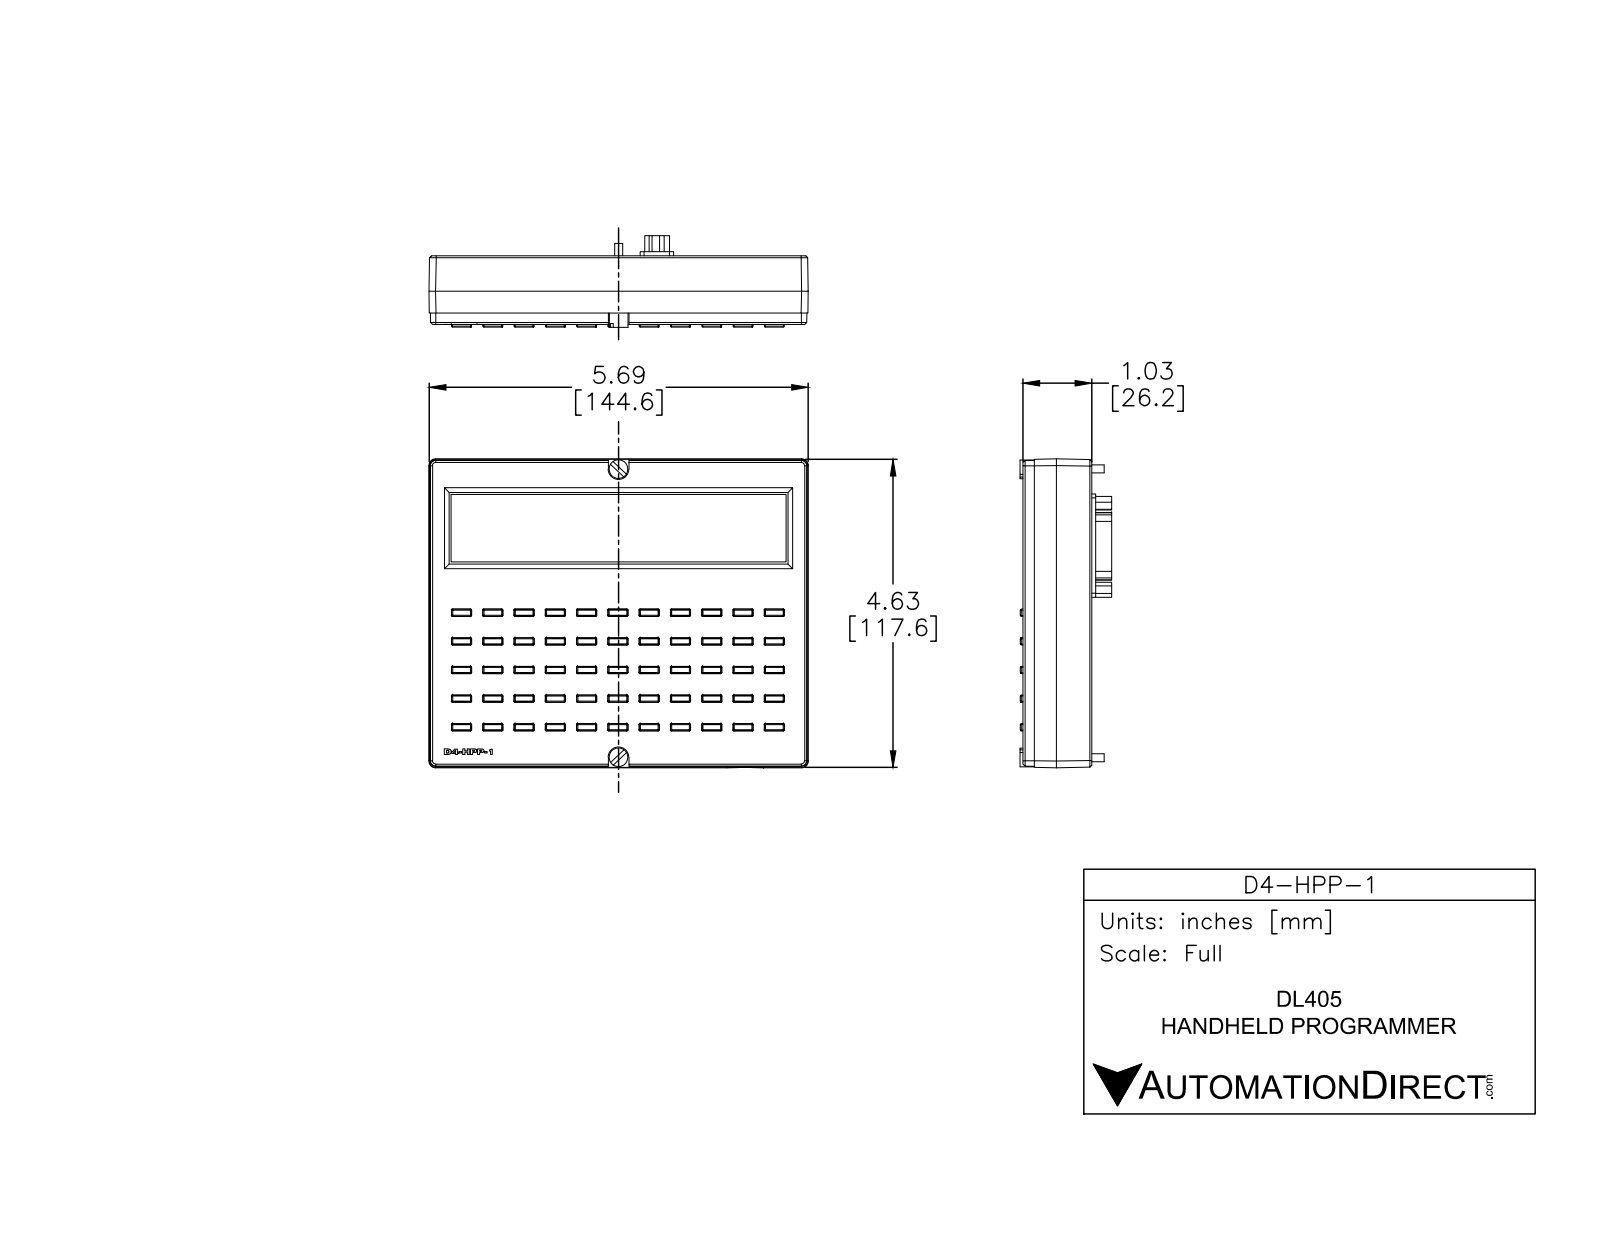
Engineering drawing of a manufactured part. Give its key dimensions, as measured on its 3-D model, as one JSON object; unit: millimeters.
{"part_name": "D4-HPP-1", "step_written_by": "SolidWorks 2014 (AUTOMOTIVE_DESIGN)", "units": "millimeters", "bodies": {"solids": 1, "faces": 1234, "planar": 486, "cylindrical": 273, "other": 475}, "overall_size": [144.8, 117.9, 35], "volume_mm3": 438500, "surface_area_mm2": 50720, "round_holes": [[2, 2], [10.1, 1], [14.2, 1]], "round_bosses_or_shafts": [[7.1, 2], [3, 2], [9.3, 1]], "partial_cylinders_radius": [[0.4, 40], [2.5, 12], [1.5, 4], [2.2, 4], [3.9, 2]], "face_to_face_distances": [26.2, 2.2, 24.1, 117.9, 144.8, 0.4, 117.5, 144.4, 1, 3.2], "hole_center_spacings": [33]}
